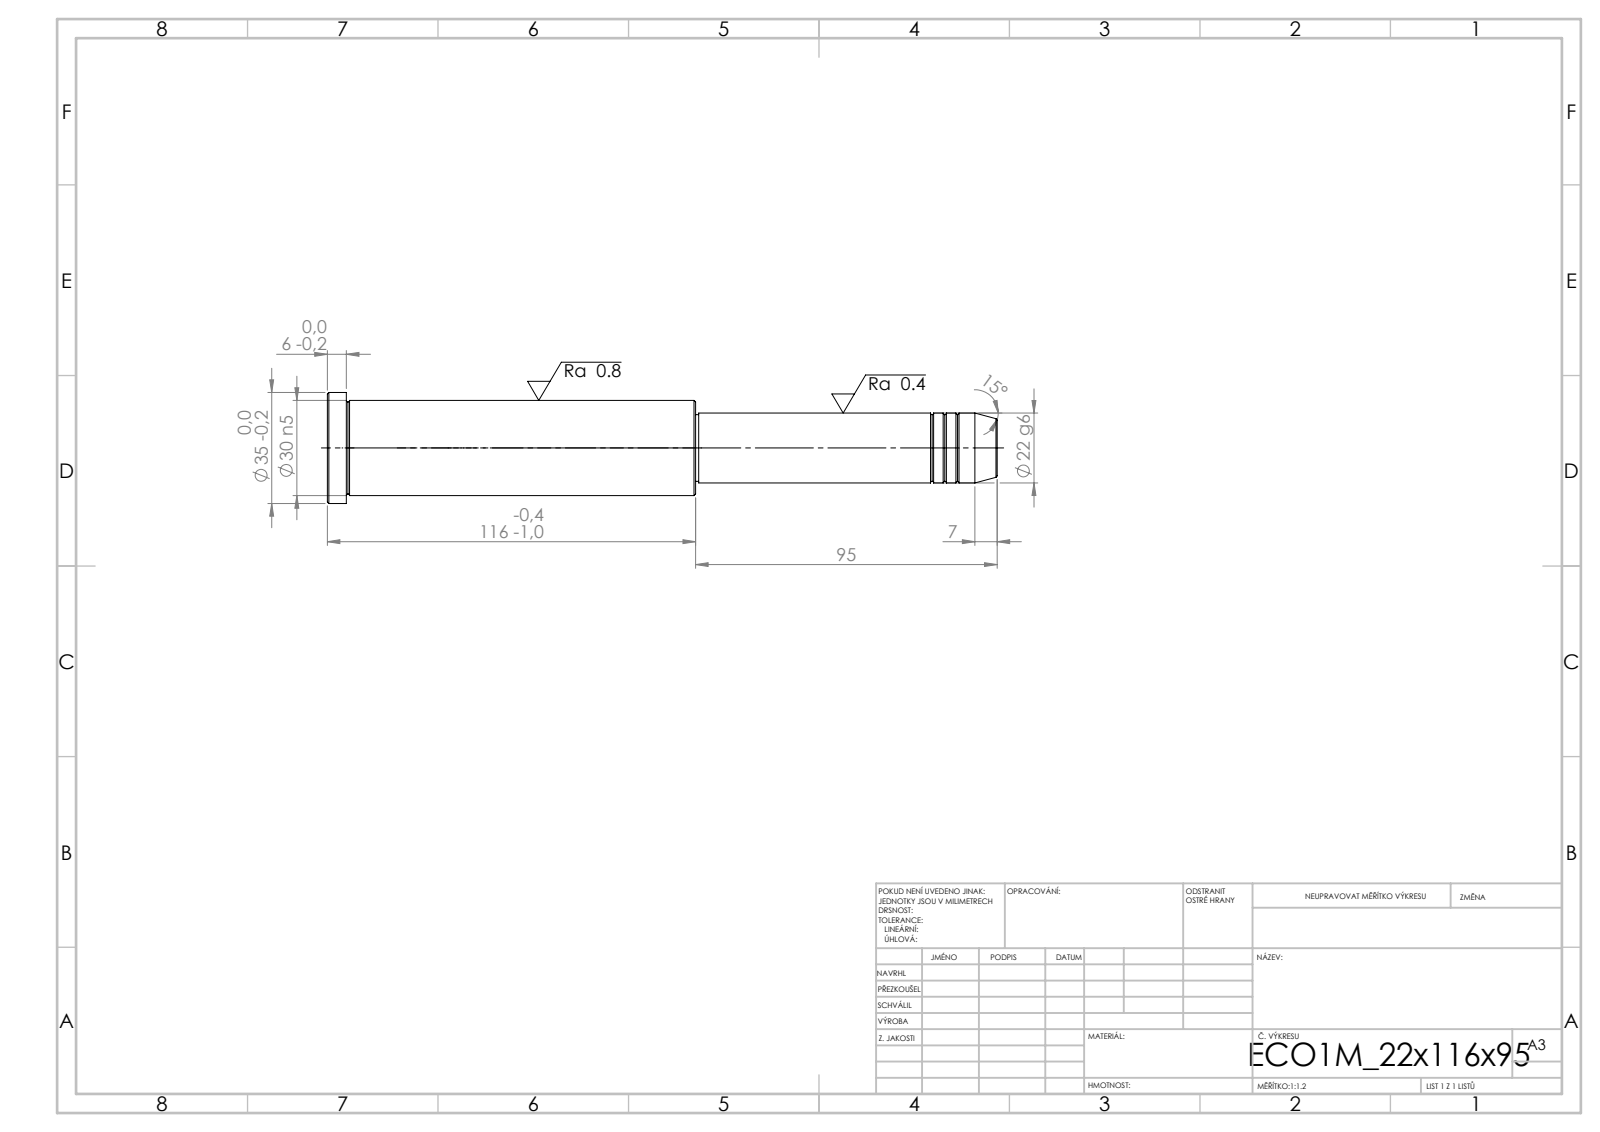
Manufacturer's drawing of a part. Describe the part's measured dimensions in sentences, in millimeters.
Its 3-D file was written by "SolidWorks 2019 (CONFIG_CONTROL_DESIGN)". It is 1 solid with 43 faces: 5 planar, 14 cylindrical and 24 other. Overall it measures 211 by 35 by 35 millimeters. Its volume is 119 035 cubic millimeters and its surface area 19 530 square millimeters. Round bosses or shafts: 1 of diameter 35, 1 of diameter 30, 1 of diameter 22, 1 of diameter 21. The main face-to-face distances are 116, 110, 6, 95, 205, 211, 94, 1, 111, 117.
